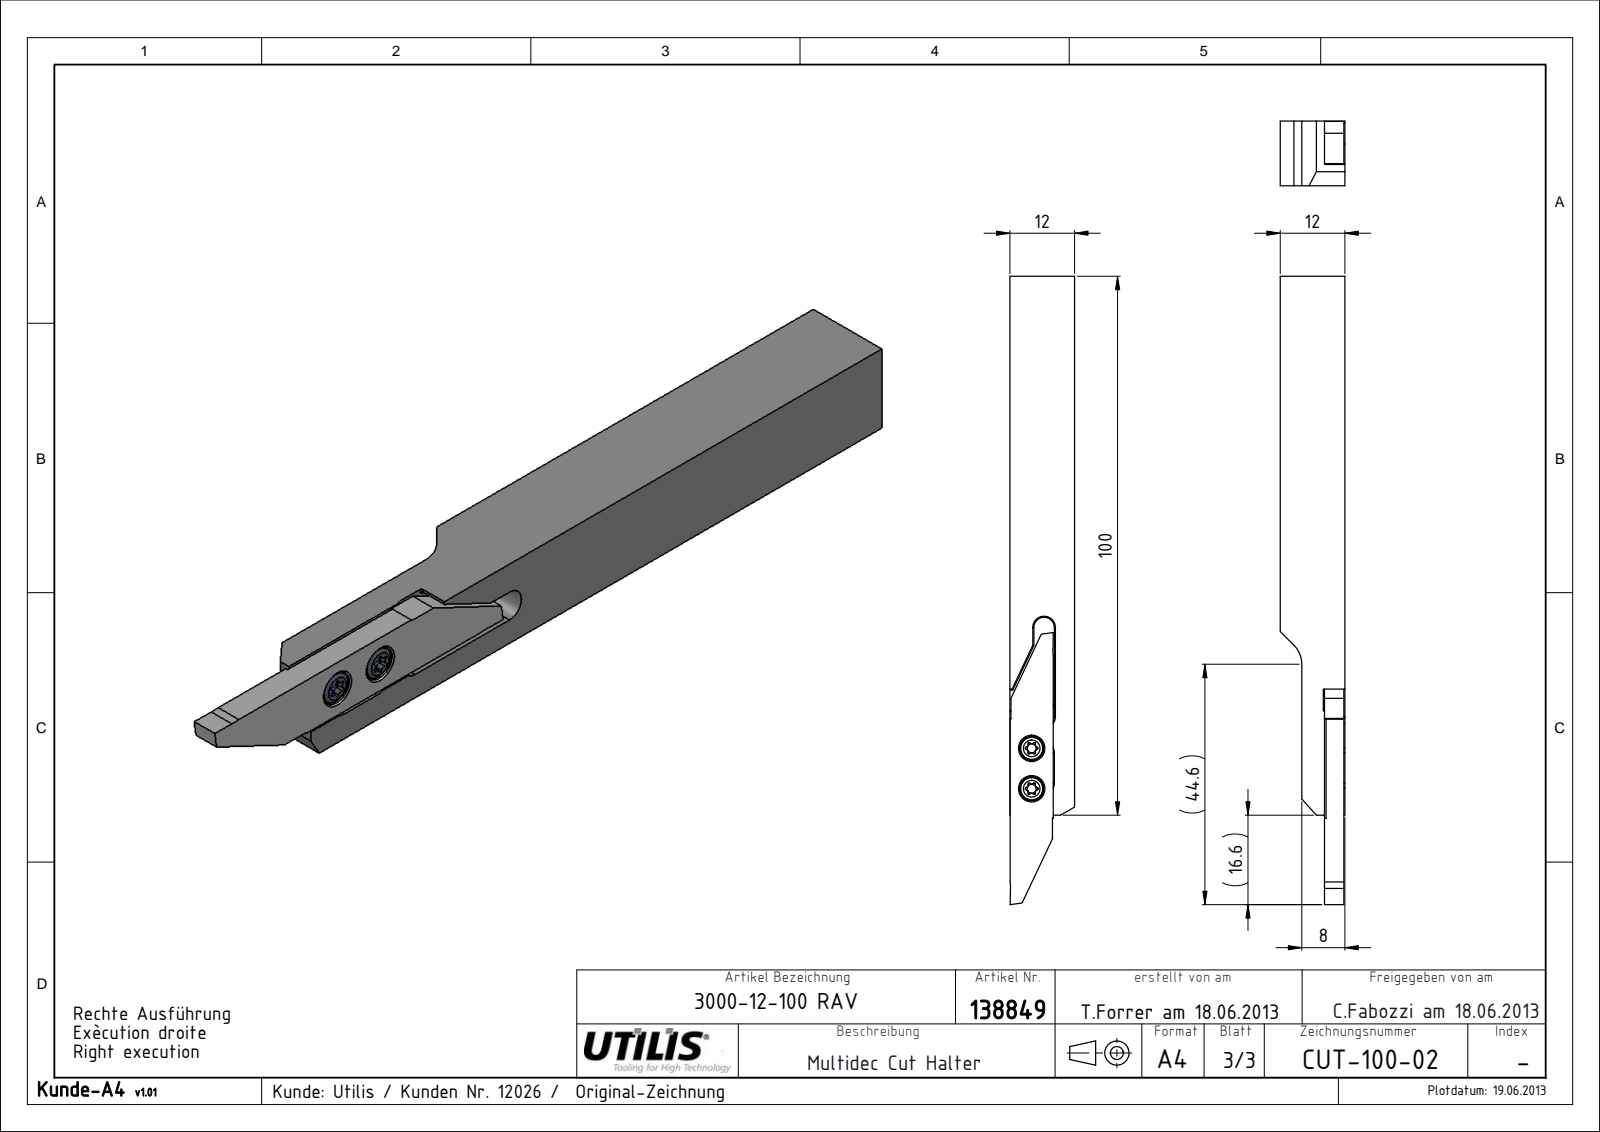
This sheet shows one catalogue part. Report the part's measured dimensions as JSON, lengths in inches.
{"part_name": "CUT- 3000 R+L Lang NUR FÜR KUNDEN _L-Lang; CUT-100-02; MSP-16_M3x7.3 T08; CUT-100-Kunde_3000-12-100 RAV", "step_written_by": "SolidWorks 2014 (CONFIG_CONTROL_DESIGN)", "units": "inches", "bodies": {"solids": 4, "faces": 118, "planar": 34, "cylindrical": 56, "other": 28}, "overall_size": [4.591, 0.472, 0.472], "volume_in3": 0.789, "surface_area_in2": 9.568, "round_holes": [[0.098, 2], [0.193, 2]], "round_bosses_or_shafts": [[0.161, 2], [0.118, 2]], "partial_cylinders_radius": [[0.008, 12], [0.018, 12], [0.083, 4], [0.394, 2], [0.197, 1]], "face_to_face_distances": [0.472, 0.323, 0.15, 0.315, 0.165, 0.157, 0.465, 0.142, 0.307, 0.156], "hole_center_spacings": [0.148, 0.295, 0.144, 0.152, 0.291, 0.299]}
